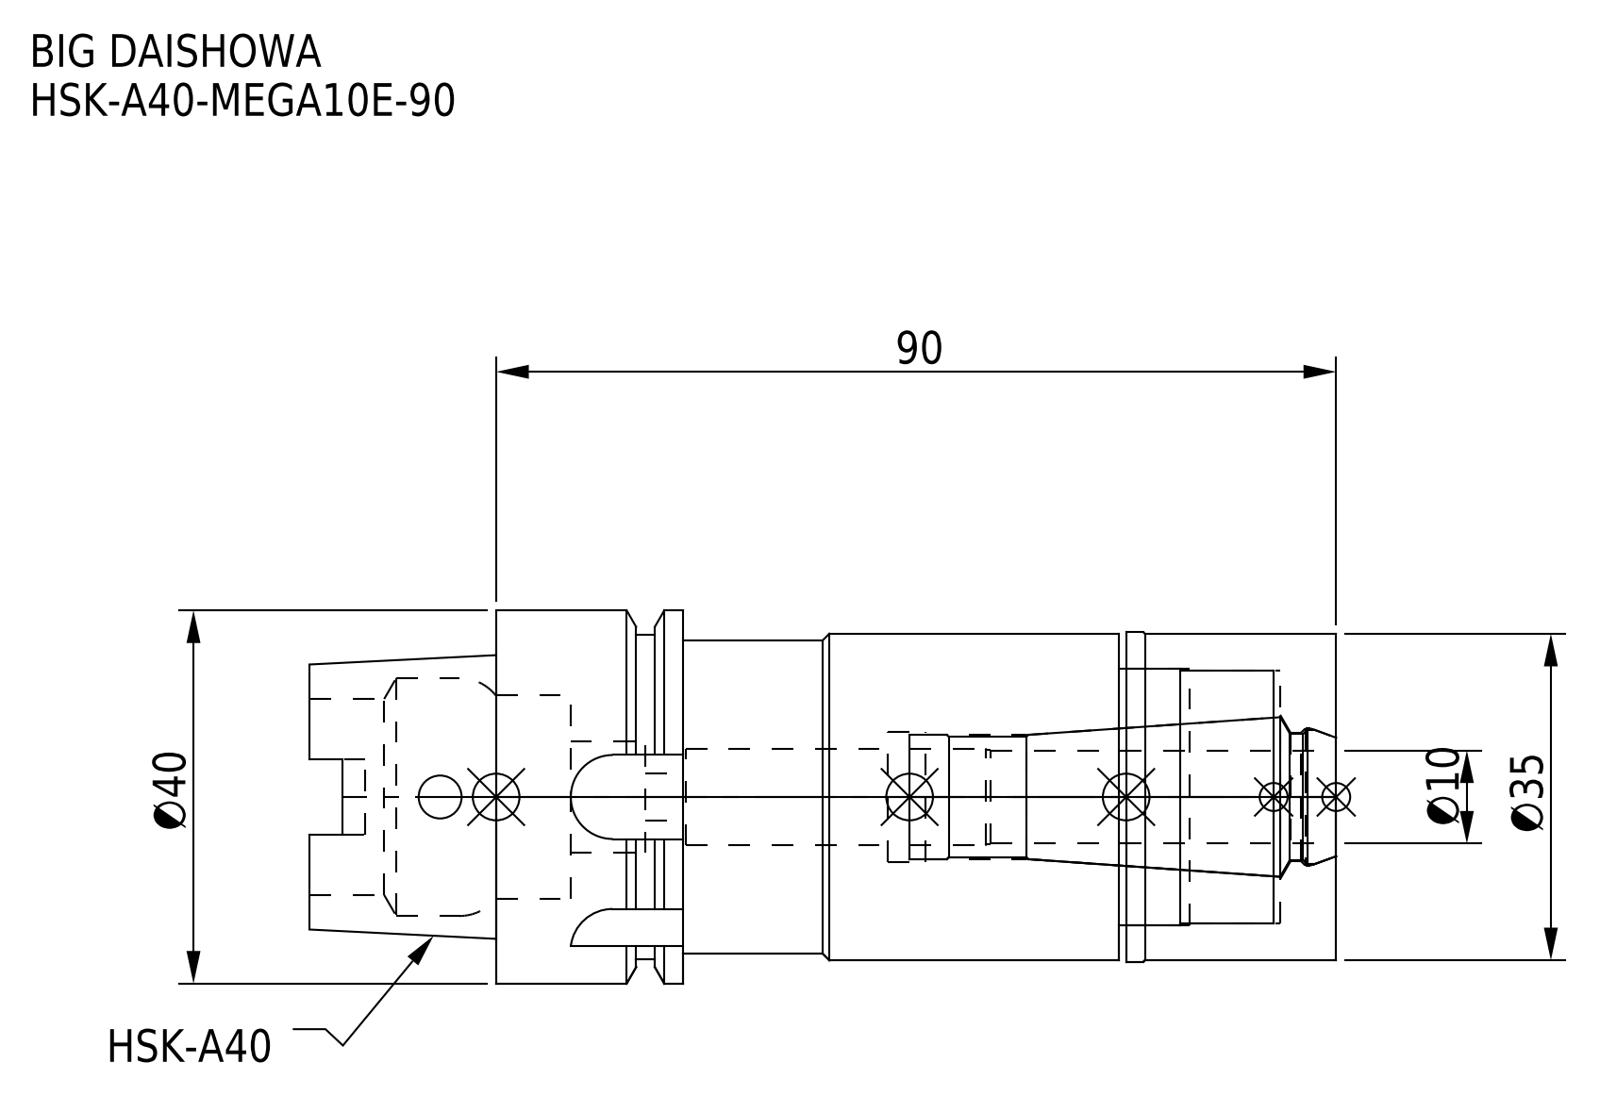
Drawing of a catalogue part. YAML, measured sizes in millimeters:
part_name: "HSK-A40-MEGA10E-90_1.stp; HSK-A40-MEGA10E-90; MEN10_1.stp; HSK-A40-MEGA10E-90-100.stp (+3 more)"
step_written_by: "SolidWorks 2019 (CONFIG_CONTROL_DESIGN)"
units: millimeters
bodies: {solids: 2, faces: 129, planar: 45, cylindrical: 58, other: 26}
overall_size: [110, 40, 40]
volume: 80140
surface_area: 24471
round_holes:
  - {diameter: 4.6, count: 1}
  - {diameter: 5, count: 1}
  - {diameter: 10.4, count: 1}
  - {diameter: 12, count: 1}
  - {diameter: 13.3, count: 1}
  - {diameter: 13.8, count: 1}
  - {diameter: 13.9, count: 1}
  - {diameter: 14.7, count: 1}
  - {diameter: 21, count: 1}
  - {diameter: 21.8, count: 1}
  - {diameter: 25.5, count: 1}
  - {diameter: 27, count: 1}
round_bosses_or_shafts:
  - {diameter: 40, count: 1}
  - {diameter: 35.3, count: 1}
  - {diameter: 35, count: 1}
  - {diameter: 34.8, count: 1}
  - {diameter: 33.6, count: 1}
partial_cylinders:
  - {radius: 1.88, count: 4}
  - {radius: 4.5, count: 4}
face_to_face_distances: [90, 20, 22.5, 67.5, 16.5, 23.3, 0.8, 66.7, 6, 84]
